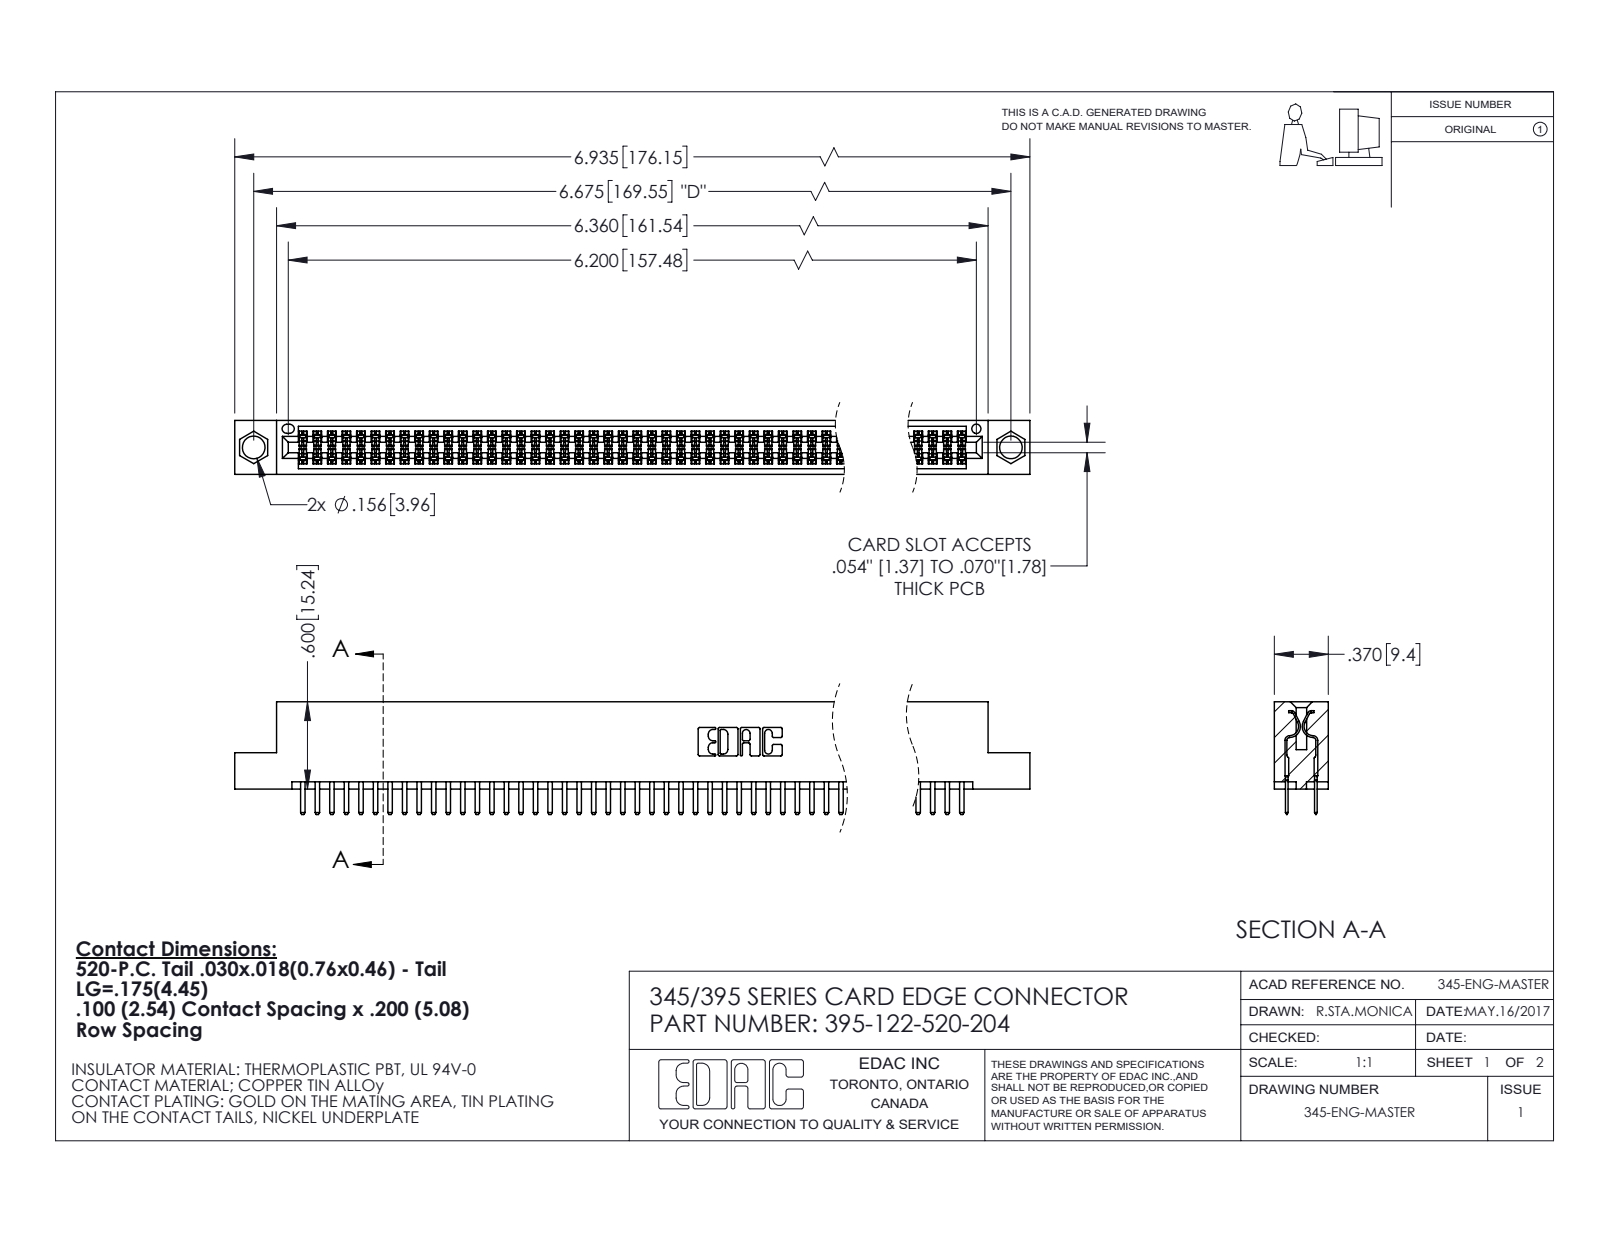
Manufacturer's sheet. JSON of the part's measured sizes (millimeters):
{"part_name": "345-292-001_345-293-120; 345 Part_Flush Mounting Lugs - 0.156 Dia-TI; 395-122-520-204", "step_written_by": "SolidWorks 2020 (CONFIG_CONTROL_DESIGN)", "units": "millimeters", "bodies": {"solids": 123, "faces": 6728, "planar": 4364, "cylindrical": 2364, "other": 0}, "overall_size": [176.1, 19.7, 9.4], "volume_mm3": 17120, "surface_area_mm2": 25430, "round_holes": [[4, 2], [1.6, 1]], "partial_cylinders_radius": [[0.2, 183], [0.3, 126], [0.3, 22], [0.2, 6], [0.8, 6], [0.7, 3], [0.4, 2], [0.5, 2]], "face_to_face_distances": [1.8, 7.6, 5.1, 9.4, 2.5, 6.9, 0.6, 5.7, 0.6, 1.8], "hole_center_spacings": [6.9, 163.6, 169.5]}
